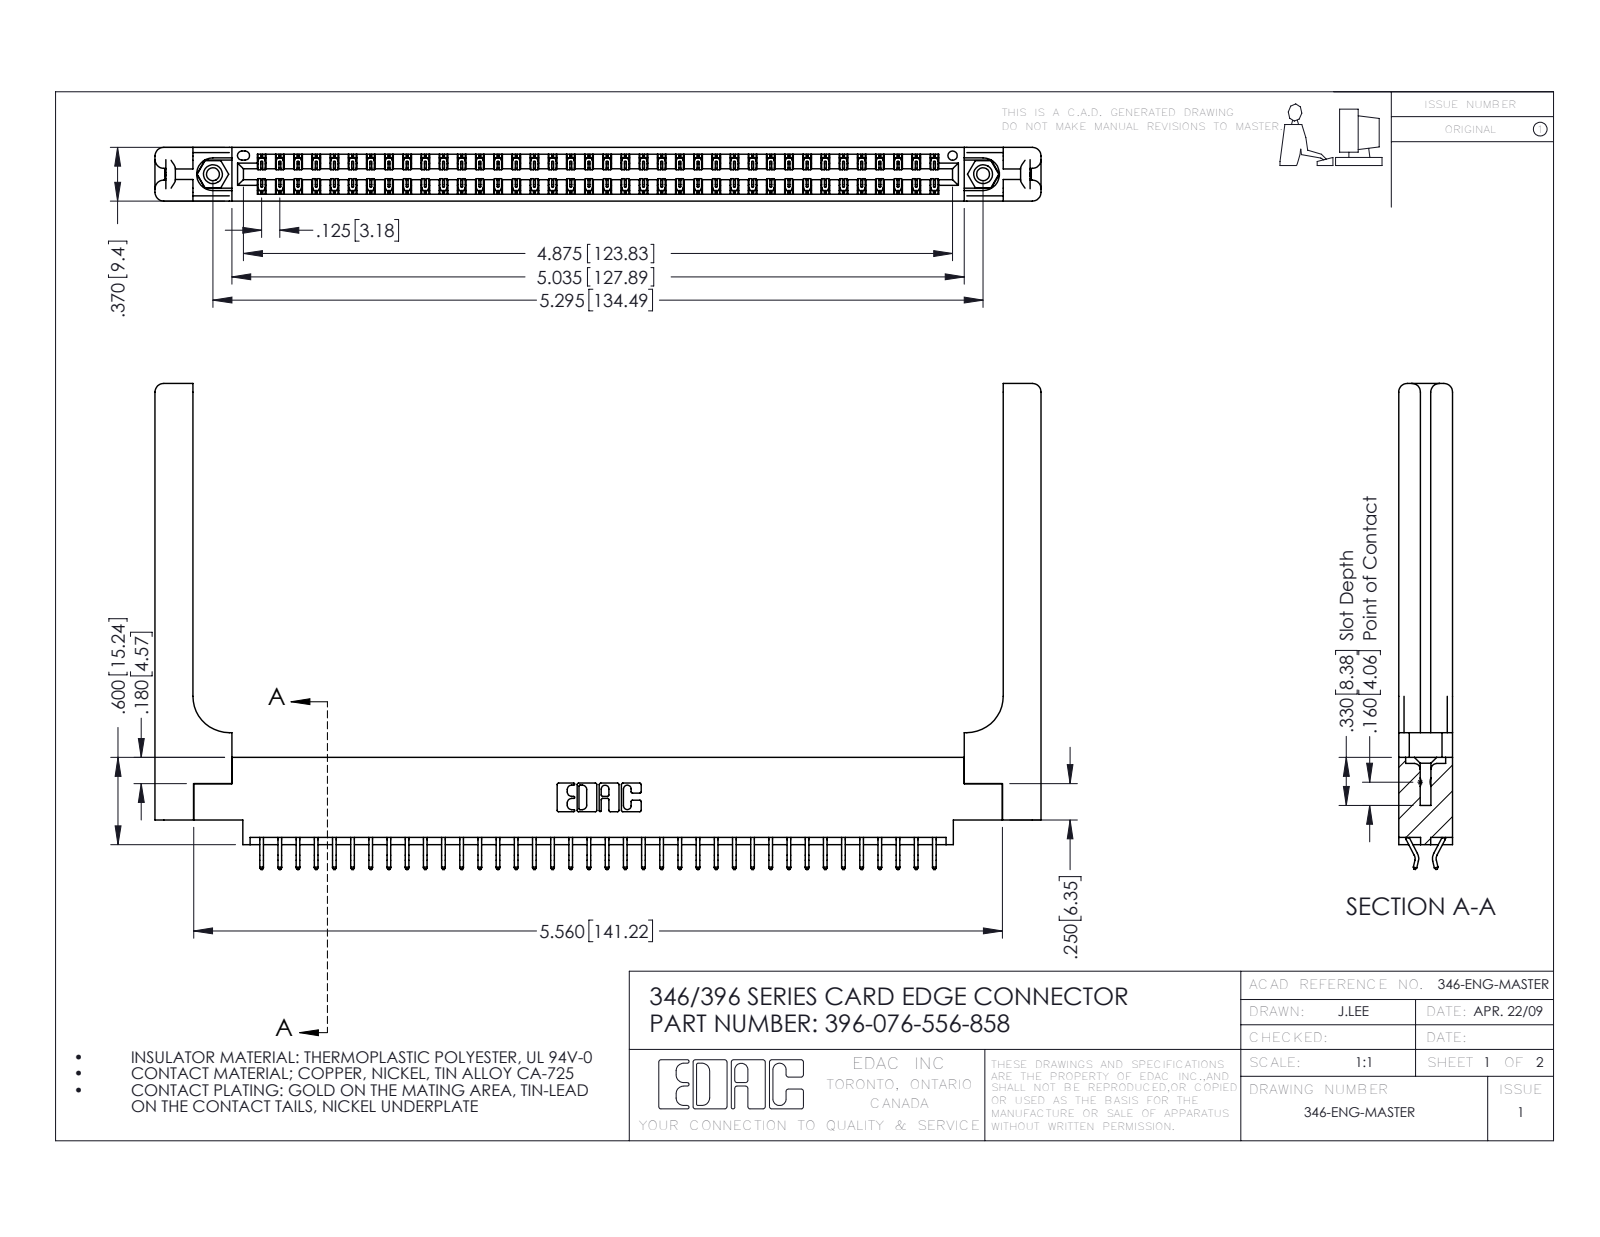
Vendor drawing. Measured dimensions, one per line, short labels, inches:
name: 346-220-058_345-220-058; 345-292-001_556 Tail; 396-076-556-858; 346 Part_0.170 Offset - 0.156 Dia-TH (+1 more)
written by: SolidWorks 2016 (CONFIG_CONTROL_DESIGN)
unit: in
bodies: 81 solids, 4790 faces (3192 planar, 1538 cylindrical, 60 other)
size: 6.091 × 3.34 × 0.37
volume: 1.366 in³; area: 39.52 in²
holes: 2× ⌀0.089, 2× ⌀0.125, 2× ⌀0.156, 1× ⌀0.064
bosses: 2× ⌀0.155
rounds: 114× R0.006, 22× R0.01, 16× R0.06, 6× R0.007, 6× R0.031, 3× R0.026, 2× R0.01, 2× R0.014
face distances: 0.37, 0.048, 0.322, 0.072, 0.148, 0.15, 0.25, 0.025, 0.298, 0.275
hole spacings: 0.246, 5.086, 5.295
